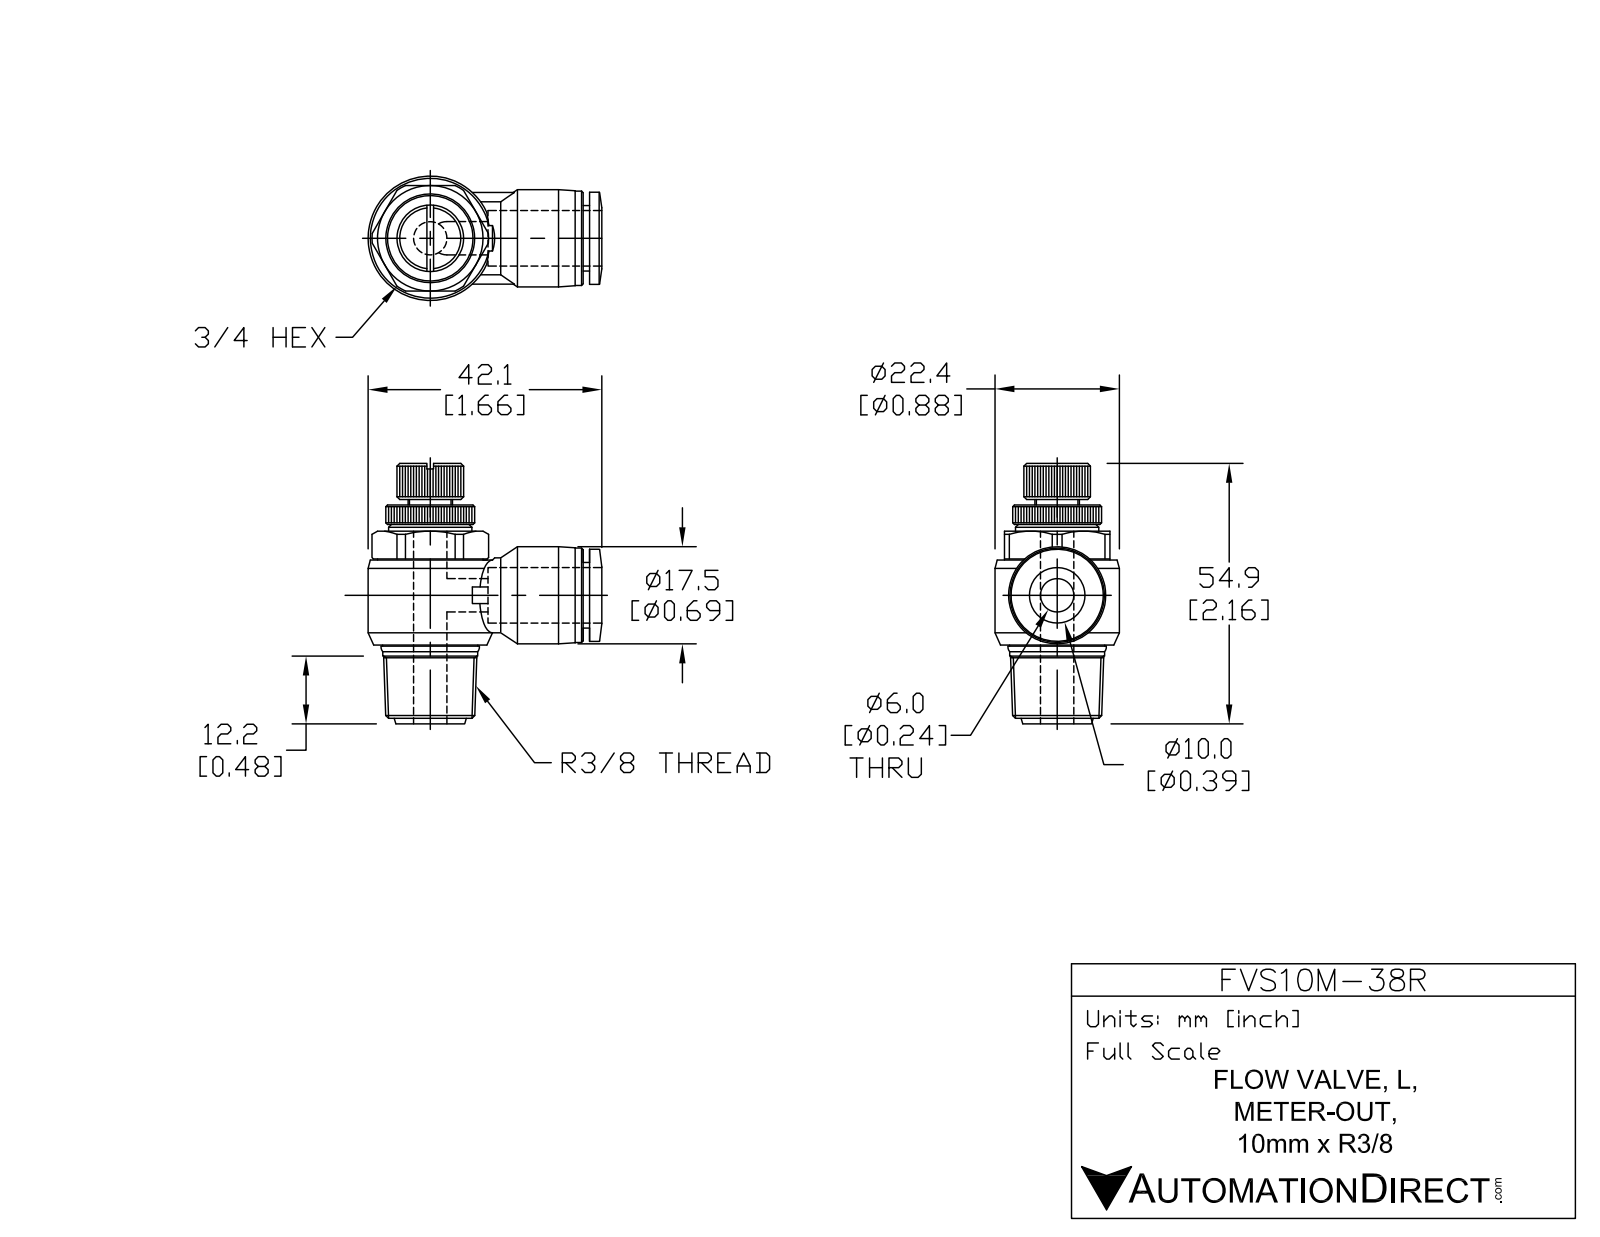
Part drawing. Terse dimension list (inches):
name: FVS10M-38R
written by: SolidWorks 2015 (AUTOMOTIVE_DESIGN)
unit: in
bodies: 1 solid, 569 faces (255 planar, 145 cylindrical, 169 other)
size: 2.236 × 1.657 × 0.882
volume: 0.91 in³; area: 9.876 in²
holes: 2× ⌀0.169, 1× ⌀0.406
bosses: 1× ⌀0.882, 1× ⌀0.748, 1× ⌀0.689, 1× ⌀0.675, 1× ⌀0.673, 1× ⌀0.669, 1× ⌀0.654, 1× ⌀0.591
rounds: 1× R0.236, 1× R0.315, 1× R0.413
face distances: 0.748, 1.035, 0.228, 1.366, 1.594, 0.602, 0.045, 0.559, 0.807, 1.161
